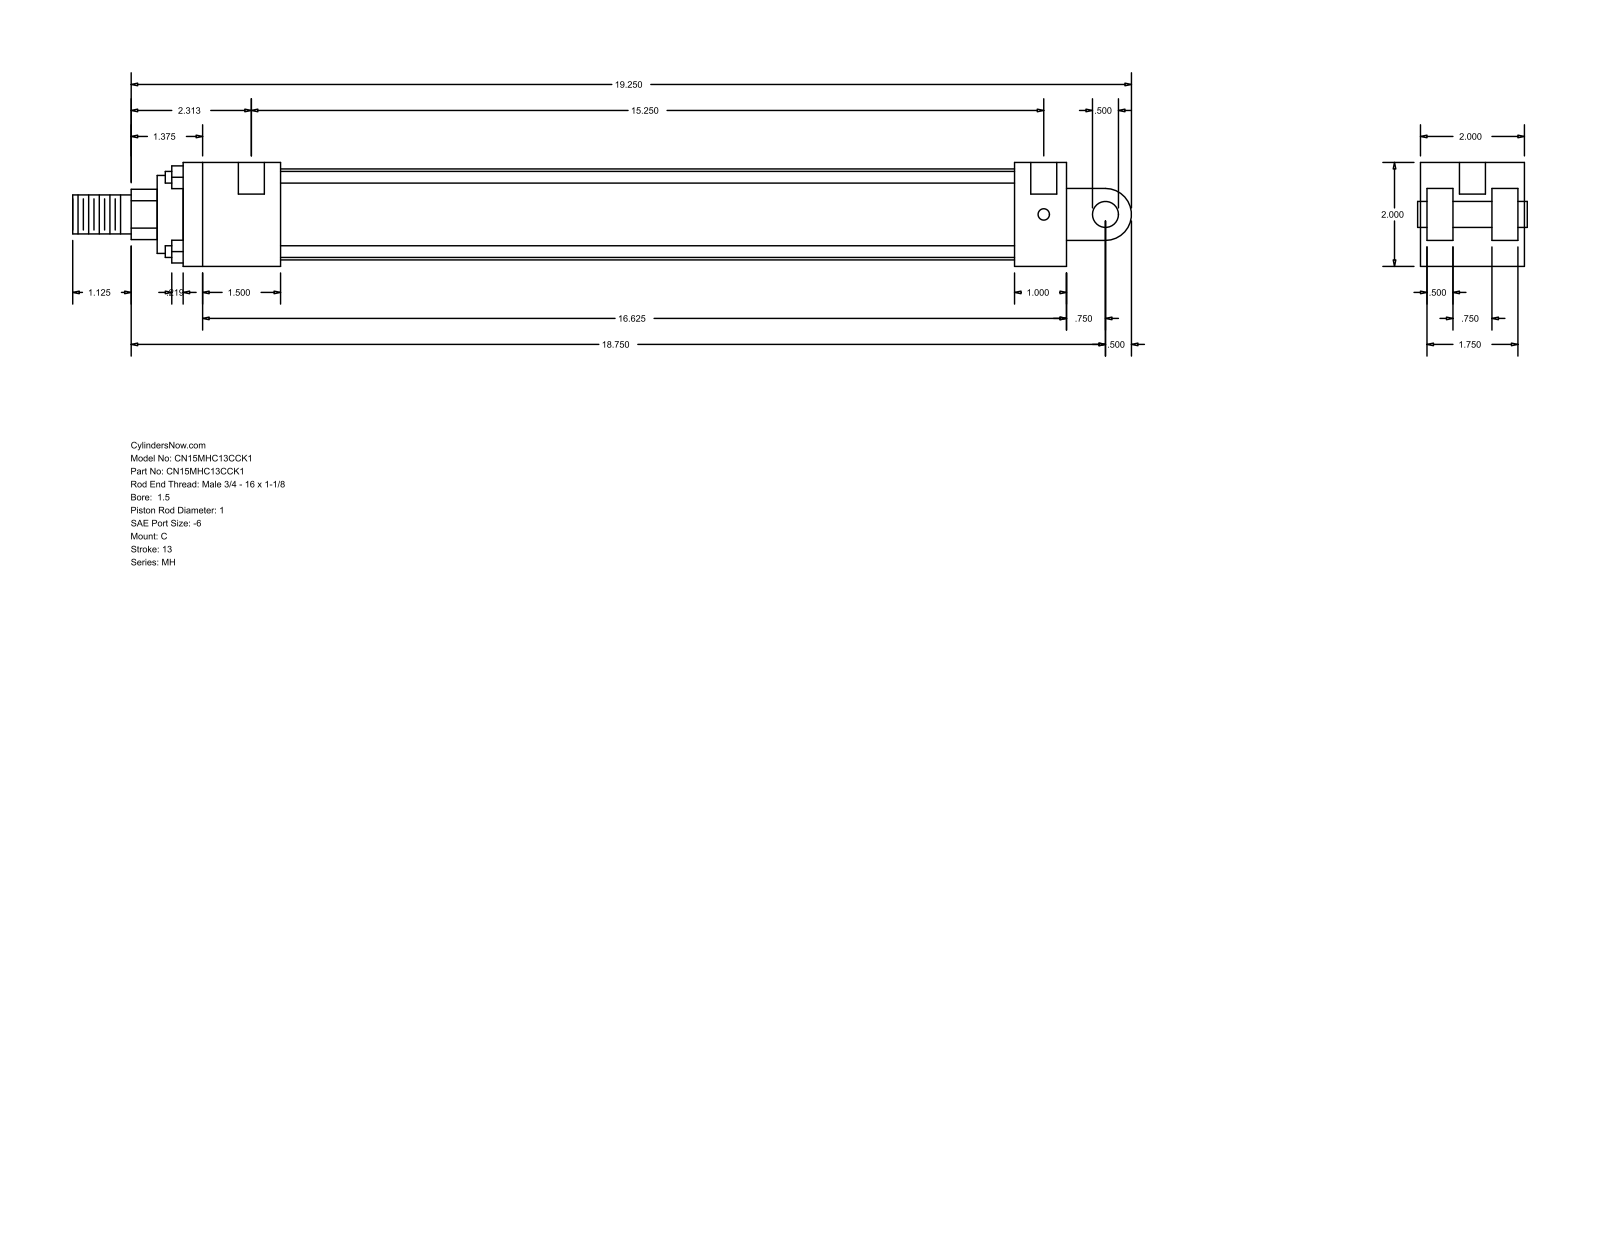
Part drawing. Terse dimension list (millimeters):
name: MH_C__0150_1
written by: GSSL Pune (CONFIG_CONTROL_DESIGN)
unit: mm
bodies: 0 solids, 99 faces (70 planar, 29 cylindrical, 0 other)
size: 517.52 × 50.8 × 50.8
holes: 4× ⌀5.56, 2× ⌀12.7
bosses: 4× ⌀5.71, 1× ⌀44.45, 1× ⌀38.1, 1× ⌀25.4, 1× ⌀19.05, 1× ⌀12.7
rounds: 1× R12.29, 1× R12.7
face distances: 50.8, 12.7, 47.63, 25.4, 3.17, 15.87, 34.93, 31.76, 431.8, 38.1
hole spacings: 390.53, 3.18, 387.35
